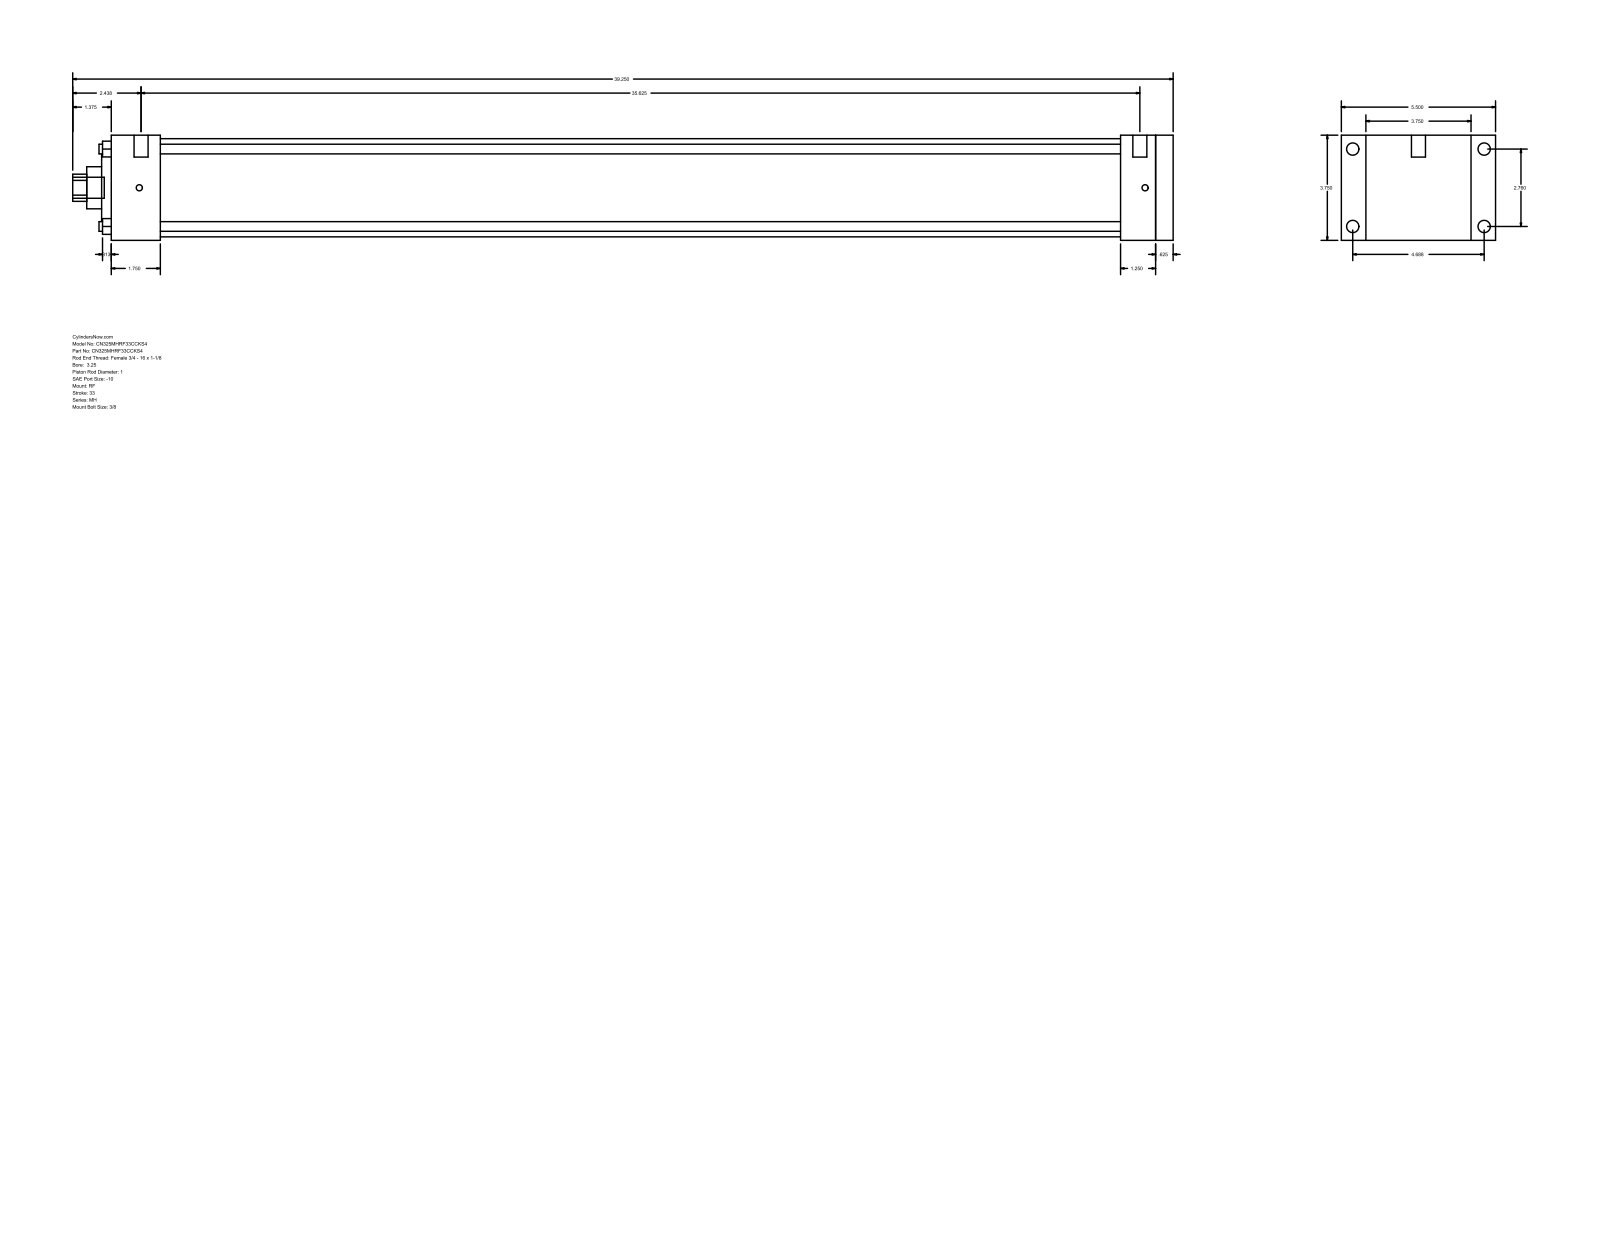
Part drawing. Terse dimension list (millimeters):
name: MH_RF__0325_1
written by: GSSL Pune (CONFIG_CONTROL_DESIGN)
unit: mm
bodies: 0 solids, 94 faces (65 planar, 29 cylindrical, 0 other)
size: 996.95 × 139.7 × 95.25
holes: 4× ⌀8.76, 1× ⌀25.4, 1× ⌀38.1, 1× ⌀60.33, 1× ⌀88.9
bosses: 4× ⌀11.13, 4× ⌀5.56, 2× ⌀12.7, 1× ⌀19.05
rounds: 1× R12.29
face distances: 95.24, 962.03, 15.87, 946.16, 22.23, 117.47, 44.46, 901.7, 917.57, 914.41
hole spacings: 49.57, 70.1, 99.14
